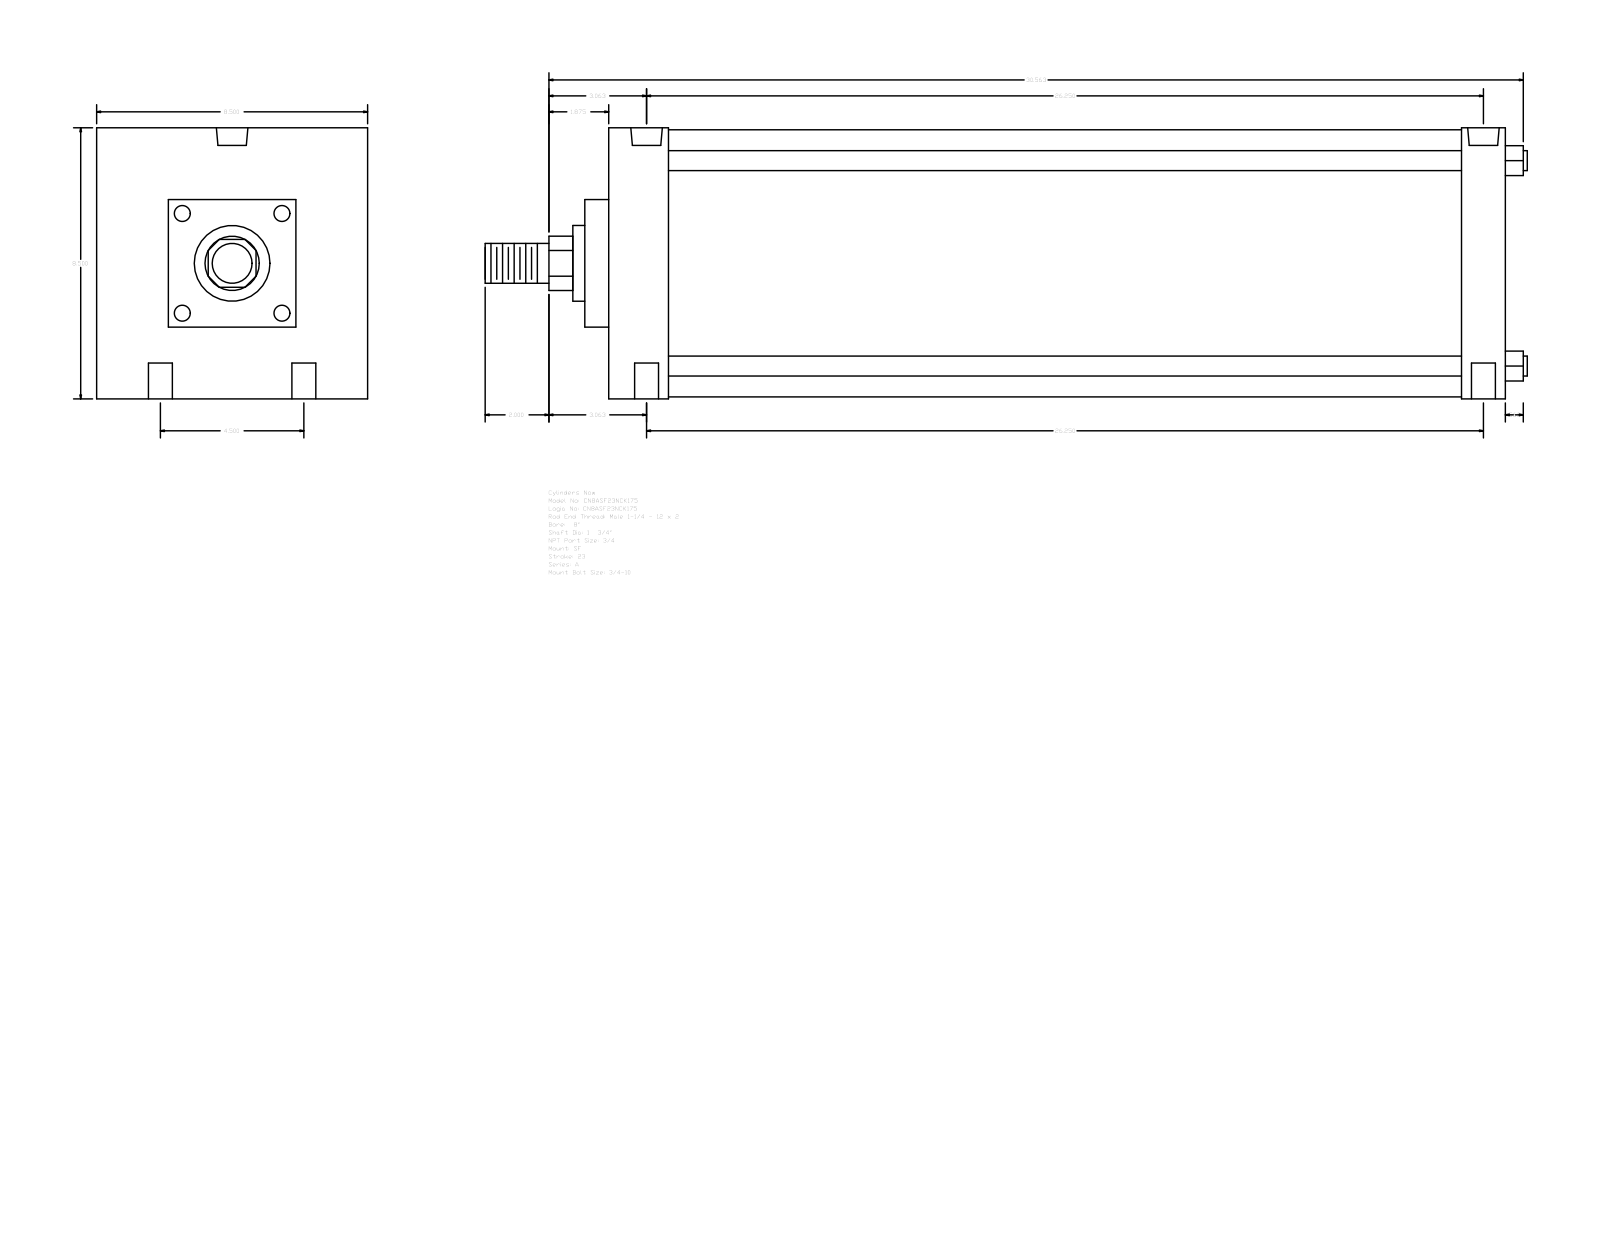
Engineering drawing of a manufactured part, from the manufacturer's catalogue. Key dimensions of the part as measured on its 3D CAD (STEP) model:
Part name (STEP PRODUCT): A_SF__0800_1.75
STEP written by: GSSL Pune (CONFIG_CONTROL_DESIGN)
Units: millimetres
Bodies: 0 solids, 93 faces (67 planar, 26 cylindrical, 0 other)
Overall size (bounding box): 830.26 × 215.9 × 215.9
Round holes (diameter × count): ⌀19.05 ×4, ⌀15.08 ×2, ⌀25.12 ×2
Round bosses / shafts (diameter × count): ⌀15.88 ×4, ⌀212.72 ×1, ⌀60.33 ×1, ⌀44.45 ×1, ⌀31.75 ×1
Partial cylindrical surfaces — rounded edges, fillets, slot ends (radius × count): R21.63 ×1
Main face-to-face distances: 714.38, 215.9, 47.63, 679.46, 631.83, 666.75, 34.92, 19.05, 158.75, 57.15
Hole centre spacings: 57.15, 669.19, 666.75, 114.3, 676.48, 654.05
